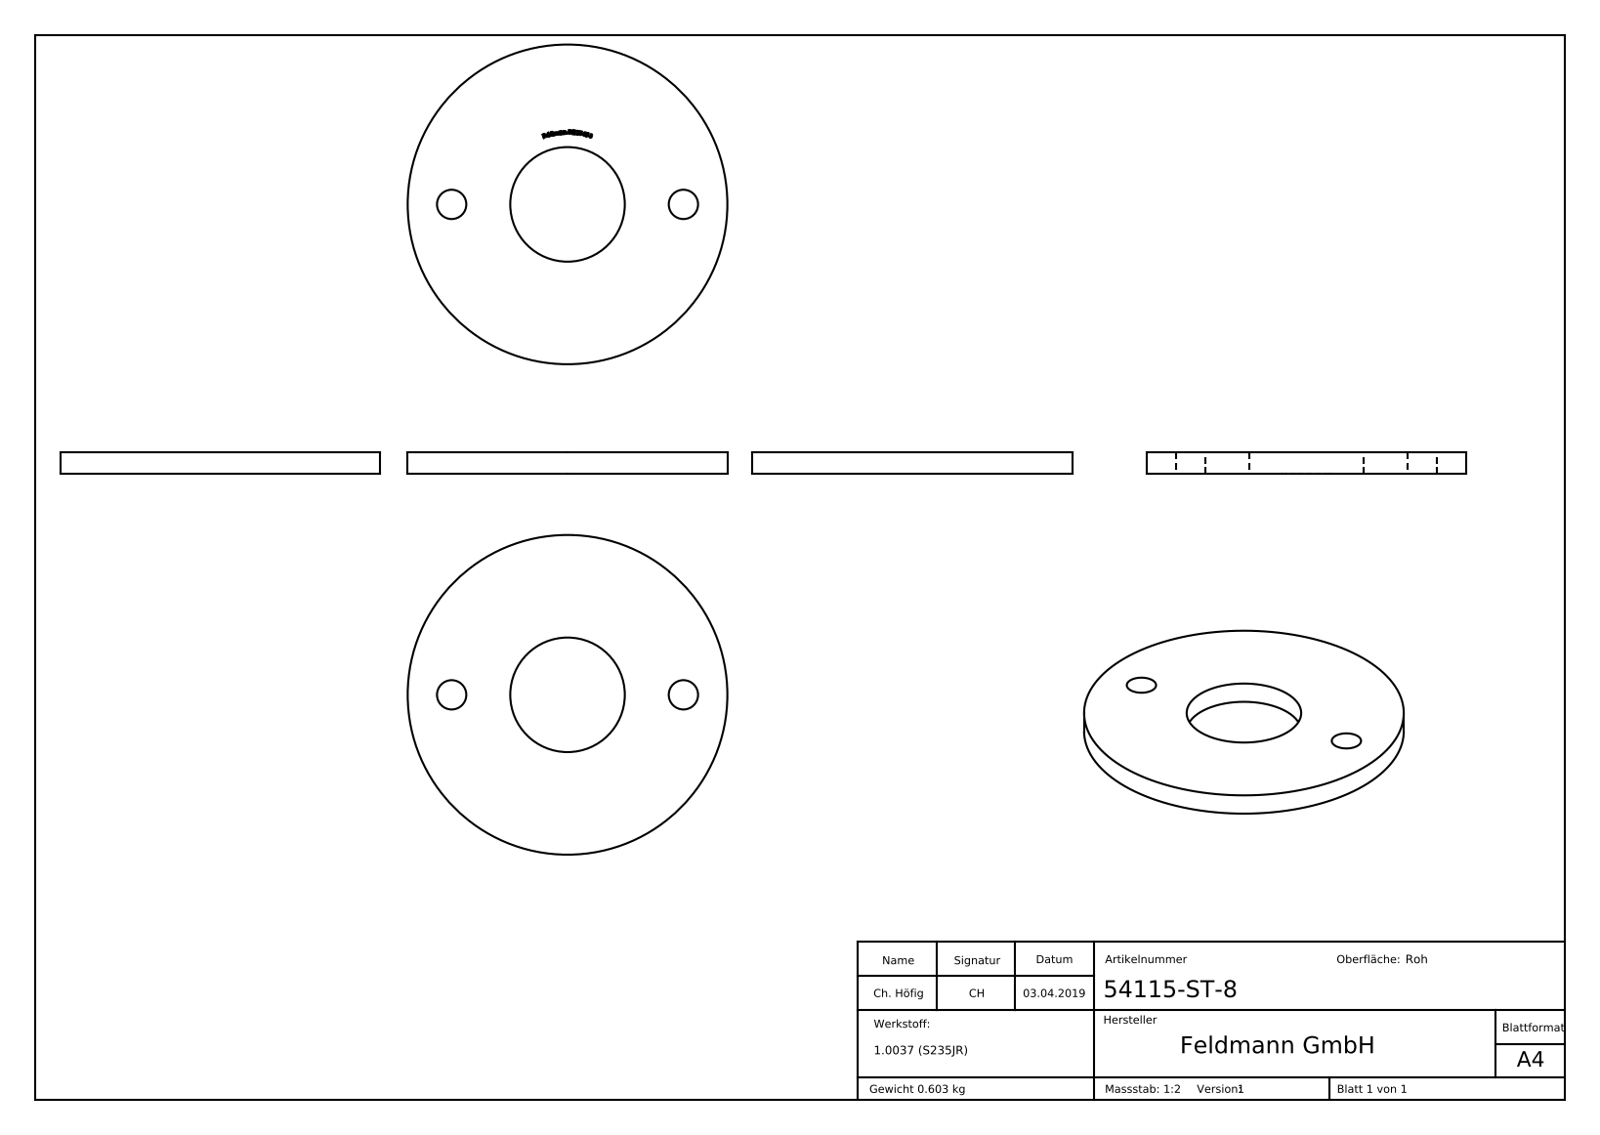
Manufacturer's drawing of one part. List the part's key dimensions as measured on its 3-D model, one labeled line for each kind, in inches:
Part name (STEP PRODUCT): 54115-ST-8
STEP written by: SolidWorks 2015 (CONFIG_CONTROL_DESIGN)
Units: inches
Bodies: 1 solid, 239 faces (135 planar, 8 cylindrical, 96 other)
Overall size (bounding box): 4.724 × 4.724 × 0.315
Volume: 4.72 in³ · Surface area: 37.19 in²
Round holes (diameter × count): ⌀0.433 ×2, ⌀1.693 ×1
Round bosses / shafts (diameter × count): ⌀4.724 ×1
Main face-to-face distances: 0.315, 0.311, 0.021, 0.033, 0.028, 0.029, 0.026, 0.024, 0.026, 0.016
Hole centre spacings: 1.713, 3.425
